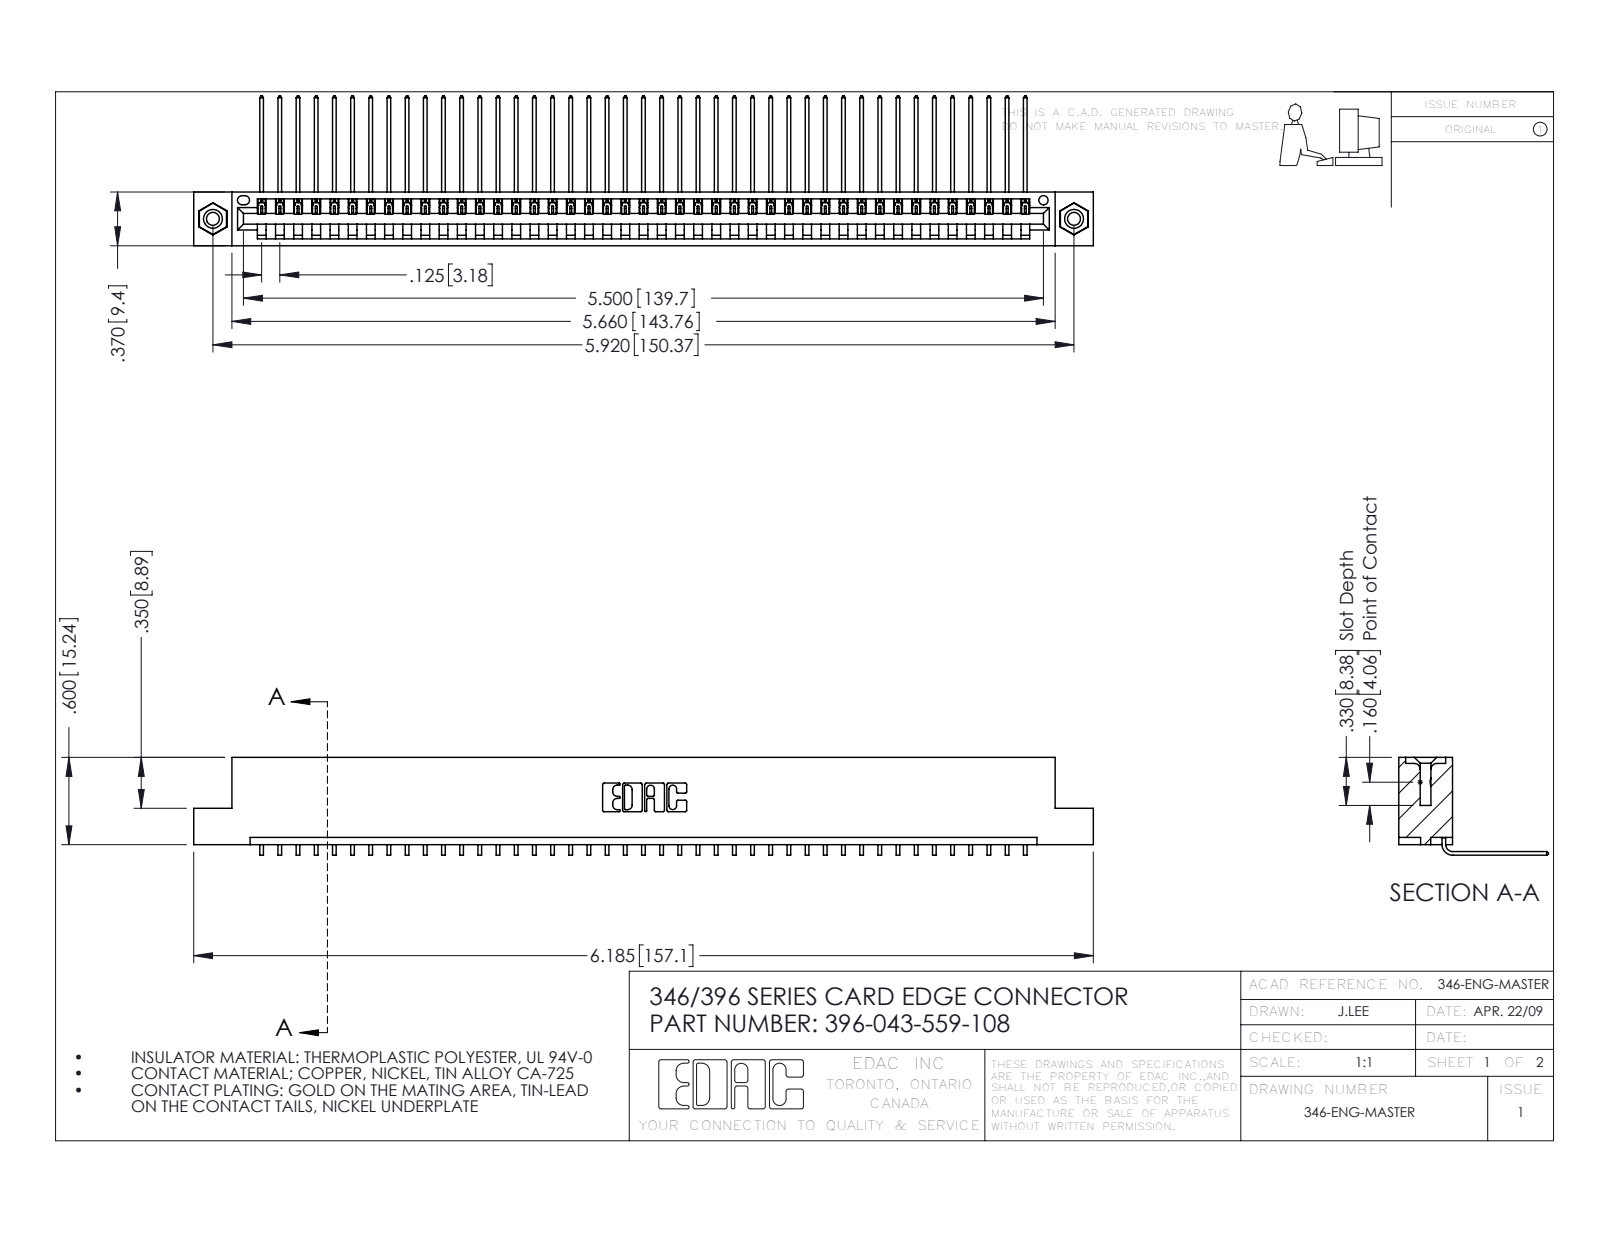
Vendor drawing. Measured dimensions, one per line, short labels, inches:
name: 346 Part_Flush Mounting Lugs - 0.156 Dia-TI; 345-250-001_345-250-003-102; 396-043-559-108; 345-292-001_558 559 Tail - 1
written by: SolidWorks 2016 (CONFIG_CONTROL_DESIGN)
unit: in
bodies: 46 solids, 2762 faces (1914 planar, 832 cylindrical, 16 other)
size: 6.185 × 1.03 × 0.673
volume: 0.926 in³; area: 30.79 in²
holes: 2× ⌀0.089, 2× ⌀0.125, 2× ⌀0.156, 1× ⌀0.064
bosses: 2× ⌀0.155
rounds: 86× R0.006, 22× R0.01, 6× R0.007, 6× R0.031, 3× R0.026, 2× R0.031, 2× R0.04, 1× R0.014
face distances: 0.048, 0.322, 0.37, 0.025, 0.25, 0.072, 0.298, 0.148, 0.222, 0.1
hole spacings: 0.246, 5.711, 5.92
